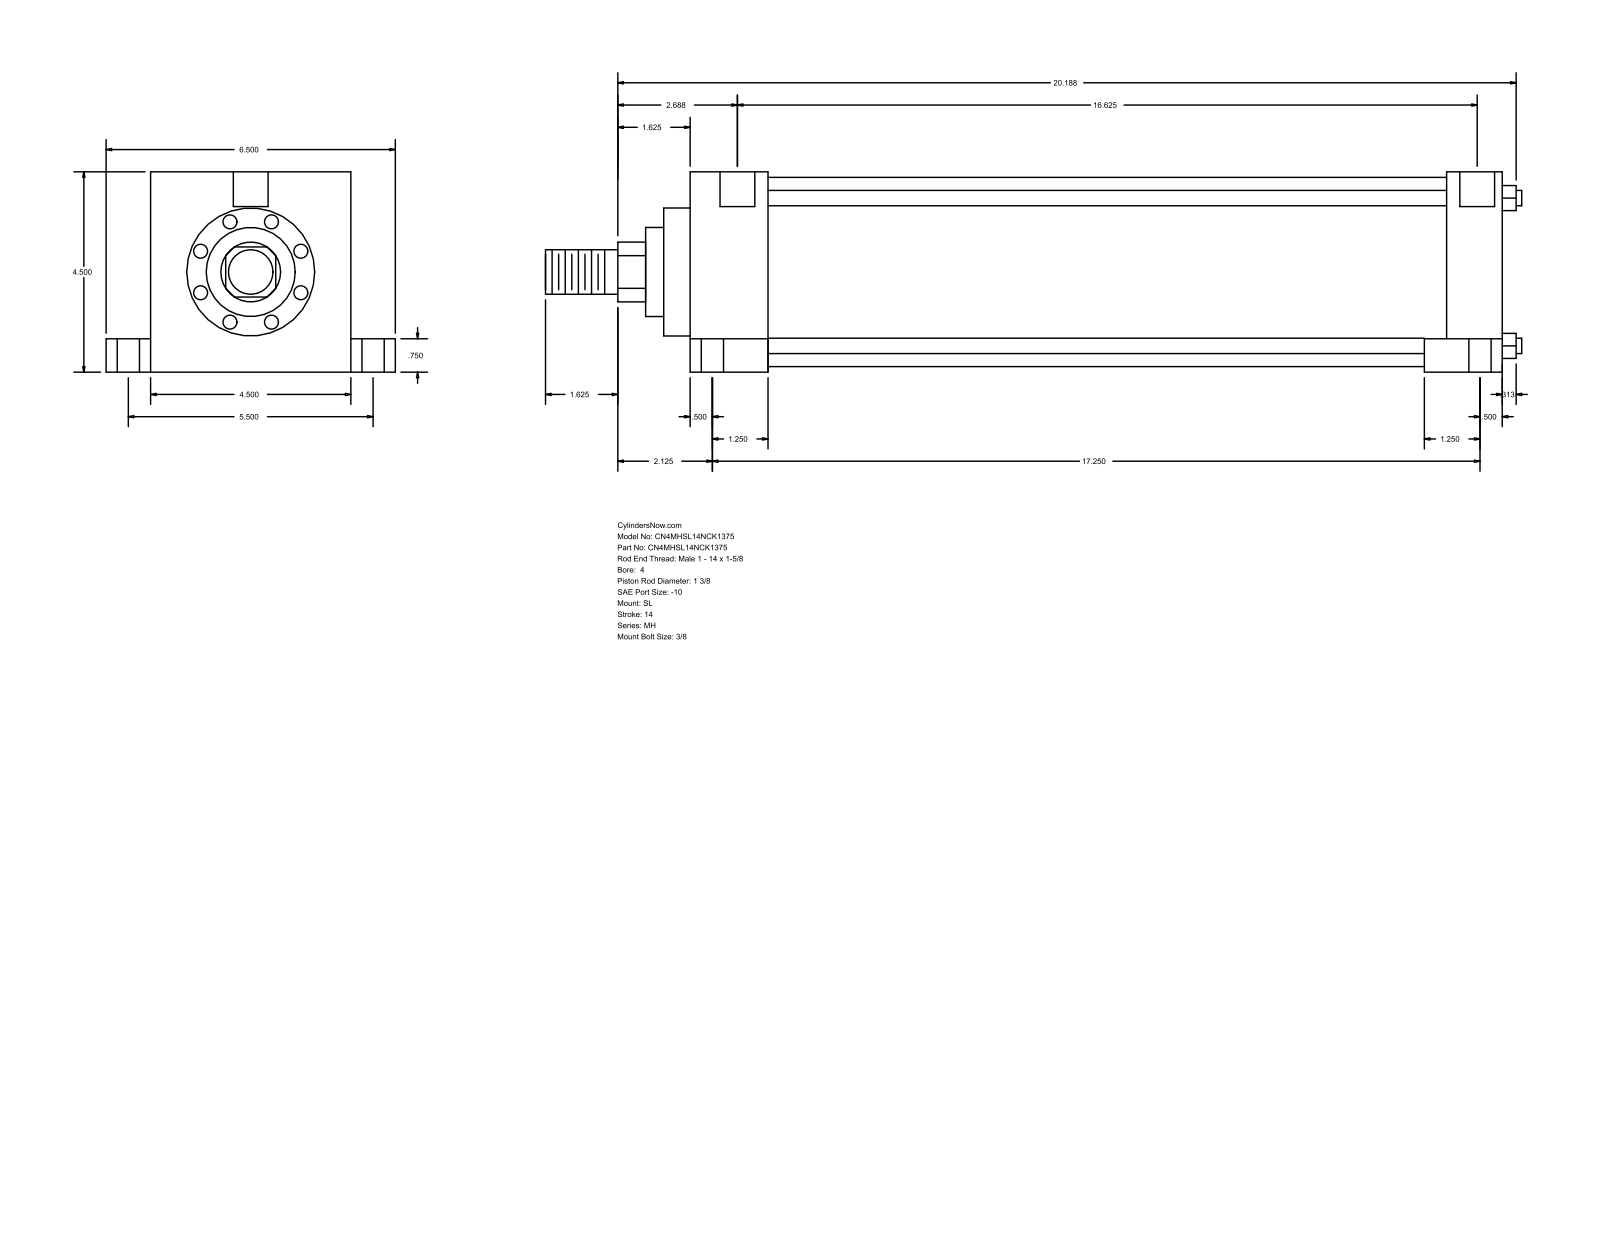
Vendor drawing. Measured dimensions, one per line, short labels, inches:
name: MH_SL__0400_1.375
written by: GSSL Pune (CONFIG_CONTROL_DESIGN)
unit: in
bodies: 0 solids, 110 faces (77 planar, 33 cylindrical, 0 other)
size: 21.937 × 6.5 × 4.5
holes: 4× ⌀0.344, 4× ⌀0.5, 4× ⌀0.75, 2× ⌀0.781
bosses: 4× ⌀0.345, 1× ⌀4.25, 1× ⌀2.875, 1× ⌀2, 1× ⌀1.375, 1× ⌀1
rounds: 1× R0.672
face distances: 4.5, 18.25, 1.75, 16.5, 17, 15.25, 1.25, 1, 5.5, 0.75
hole spacings: 2.75, 2.751, 2.795, 2.807, 5.5, 16.75, 16.913, 16.974
